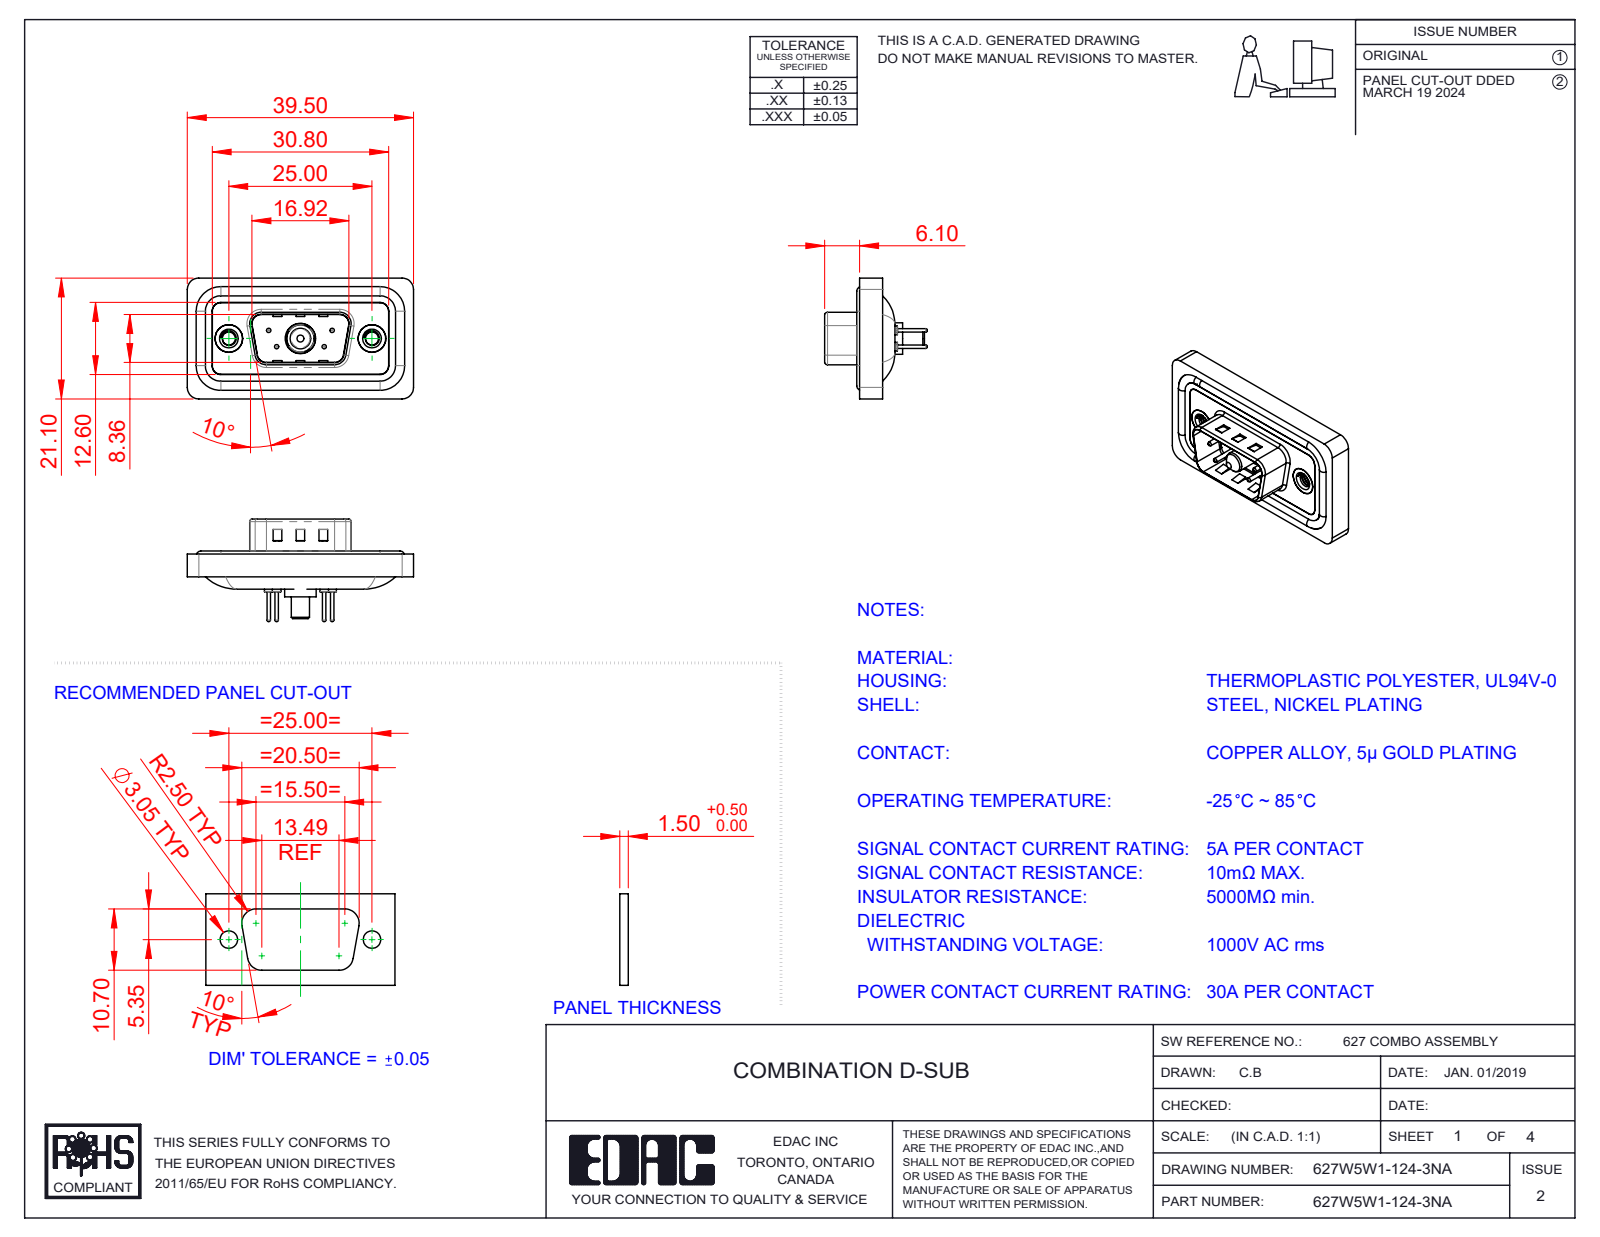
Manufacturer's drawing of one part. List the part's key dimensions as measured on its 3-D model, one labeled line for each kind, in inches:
Part name (STEP PRODUCT): 627Combo Threaded Rivet_A; 627Combo Contact Row 1_24; Power Pin_30A S; 627Combo Shell Rear_09 Contacts (+5 more)
STEP written by: SolidWorks 2023 (CONFIG_CONTROL_DESIGN)
Units: inches
Bodies: 13 solids, 596 faces (183 planar, 257 cylindrical, 156 other)
Overall size (bounding box): 1.555 × 0.831 × 0.705
Volume: 0.268 in³ · Surface area: 10.76 in²
Round holes (diameter × count): ⌀0.03 ×4, ⌀0.063 ×4, ⌀0.079 ×4, ⌀0.089 ×2, ⌀0.157 ×2, ⌀0.189 ×2, ⌀0.197 ×2, ⌀0.191 ×1, ⌀0.209 ×1
Round bosses / shafts (diameter × count): ⌀0.063 ×4, ⌀0.059 ×4, ⌀0.024 ×4, ⌀0.193 ×2, ⌀0.217 ×1, ⌀0.205 ×1, ⌀0.187 ×1, ⌀0.148 ×1
Partial cylindrical surfaces — rounded edges, fillets, slot ends (radius × count): R0.059 ×22, R0.079 ×18, R0.02 ×8, R0.063 ×8, R0.01 ×4, R0.024 ×4, R0.026 ×4, R0.035 ×4
Main face-to-face distances: 0.016, 0.043, 0.114, 0.063, 0.122, 0.059, 0.02, 0.098, 0.157, 0.031
Hole centre spacings: 0.124, 0.225, 0.28, 0.492, 0.713, 0.173, 0.173, 0.327
